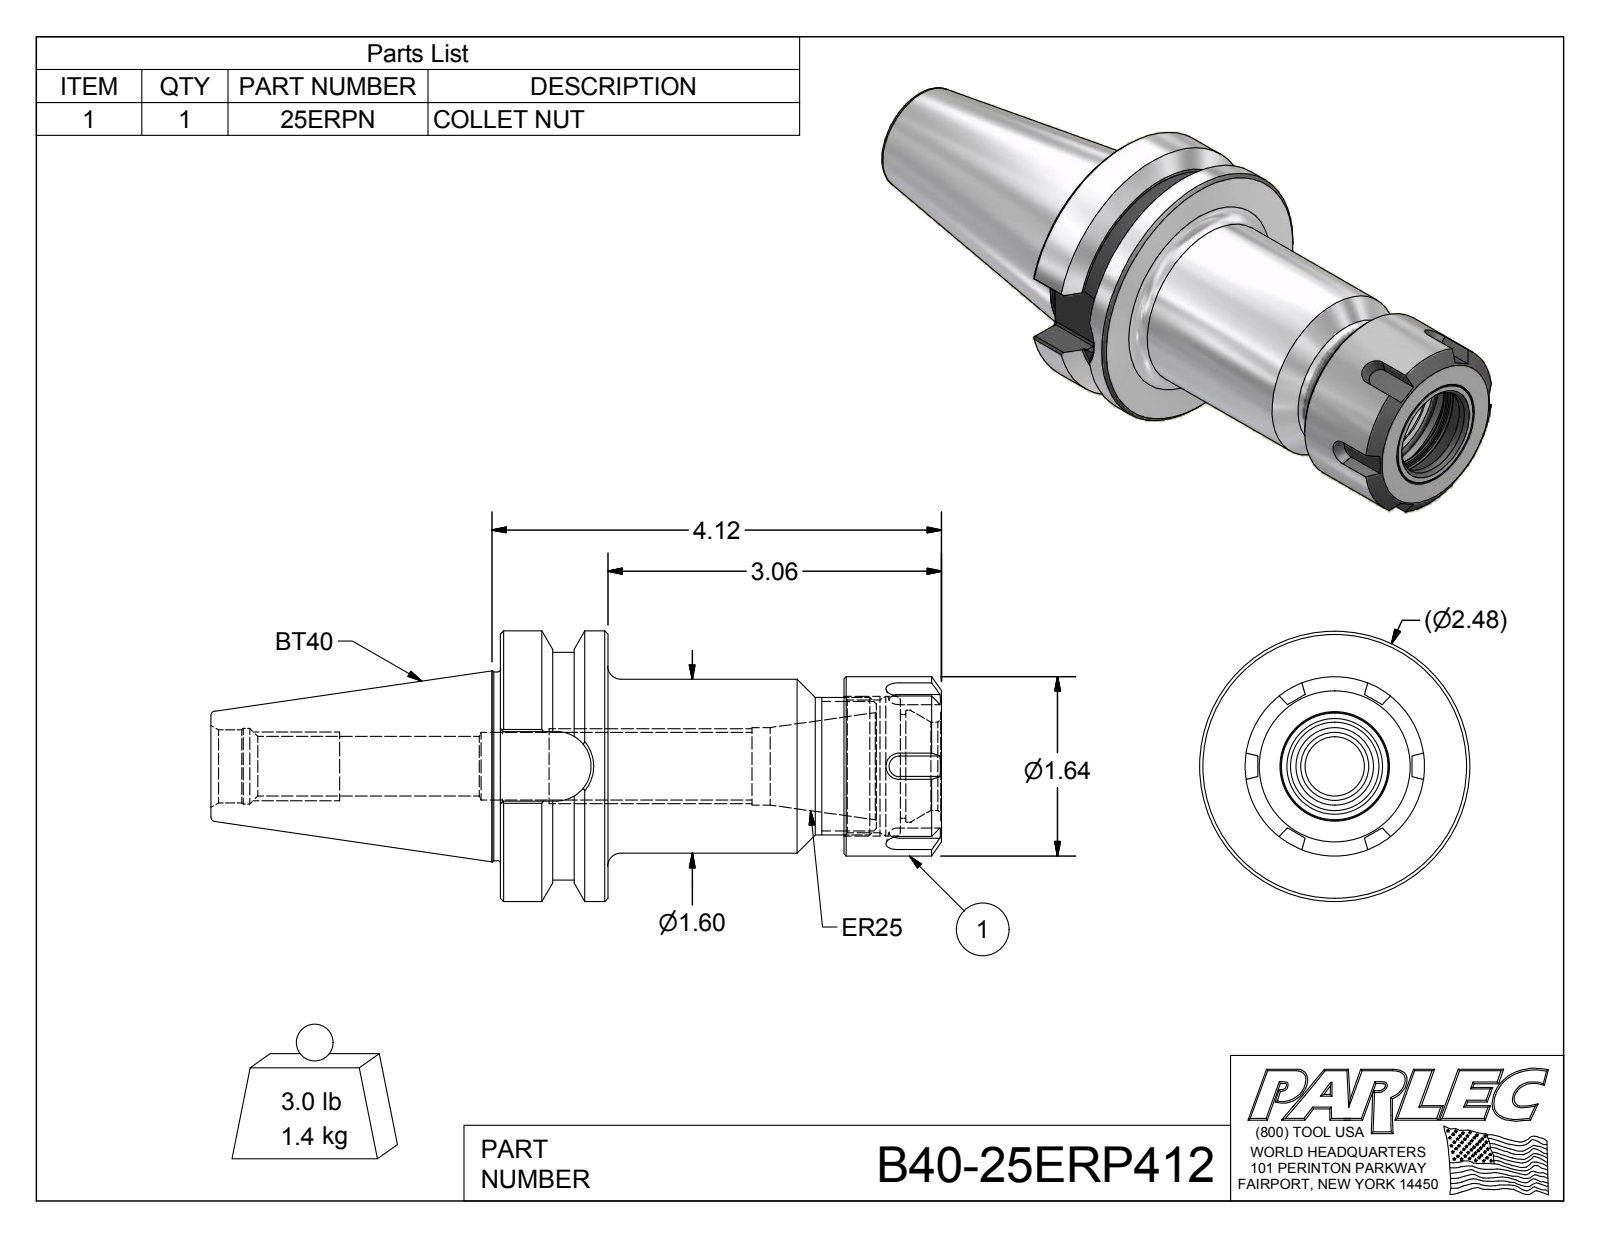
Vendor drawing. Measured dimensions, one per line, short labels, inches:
name: B40-25ERP412; B40-25ER4-1; 25ERPN
written by: Autodesk Inventor 2012 (AUTOMOTIVE_DESIGN)
unit: in
bodies: 2 solids, 119 faces (47 planar, 29 cylindrical, 43 other)
size: 6.695 × 2.48 × 2.48
volume: 11.56 in³; area: 61.72 in²
holes: 1× ⌀0.545, 1× ⌀0.62, 1× ⌀0.67, 1× ⌀0.694, 1× ⌀0.71, 1× ⌀0.811, 1× ⌀0.95, 1× ⌀1.027, 1× ⌀1.217, 1× ⌀1.28
bosses: 1× ⌀2.48, 1× ⌀2.087, 1× ⌀1.73, 1× ⌀1.643, 1× ⌀1.595, 1× ⌀1.26
rounds: 8× R0.02, 1× R0.319
face distances: 0.984, 4.042, 3.058, 3.149, 2.165, 0.893, 1.78, 3.667, 2.683, 0.518
